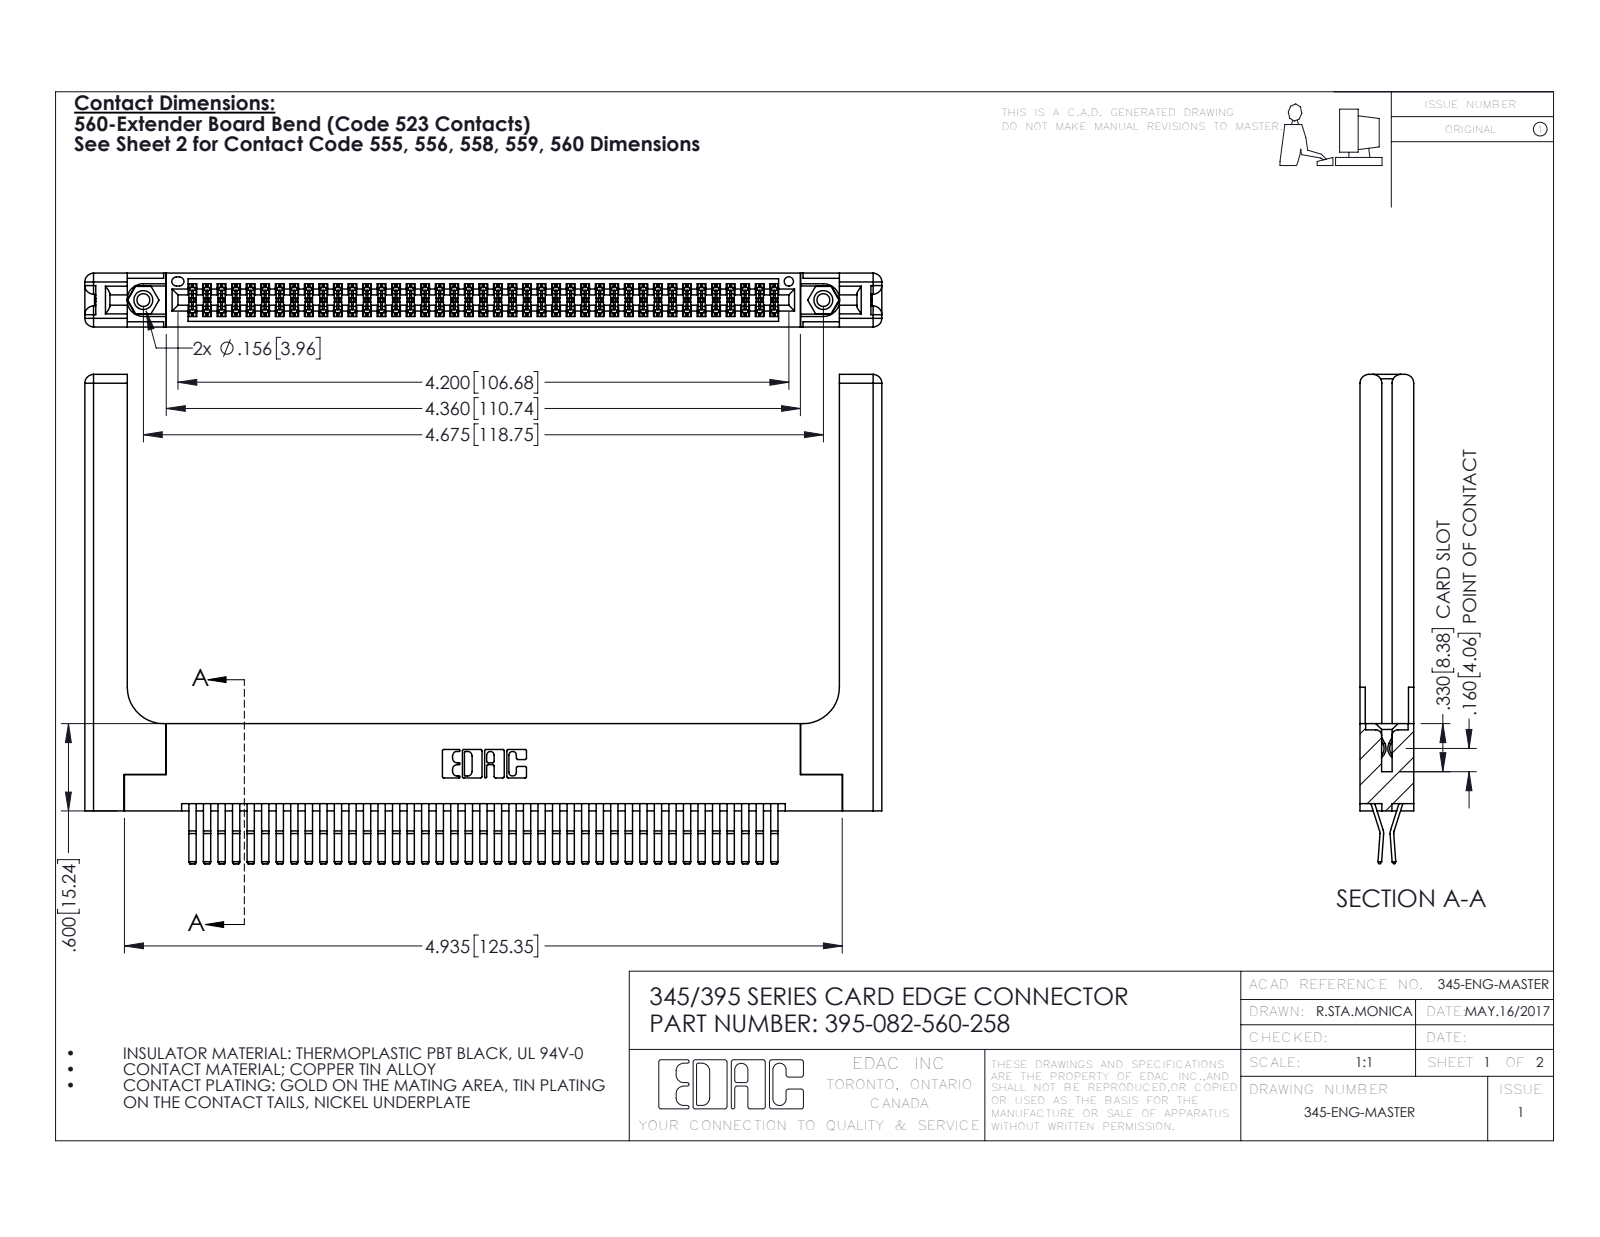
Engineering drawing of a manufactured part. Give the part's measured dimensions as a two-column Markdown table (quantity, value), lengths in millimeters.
| quantity | value |
| --- | --- |
| part name | 345-292-001_560 Tail; 395-082-560-258; 345-220-058_345-220-058; 345-250-001_345-250-001-102 (+1 more) |
| STEP written by | SolidWorks 2016 (CONFIG_CONTROL_DESIGN) |
| units | millimeters |
| bodies | 87 solids, 4646 faces (2934 planar, 1652 cylindrical, 60 other) |
| overall size | 139.2 × 85.4 × 9.4 |
| volume | 22 520 mm³ |
| surface area | 27 190 mm² |
| round holes (diameter × count) | 2.3 × 2, 3.2 × 2, 4 × 2, 1.6 × 1 |
| round bosses / shafts (diameter × count) | 3.9 × 2 |
| partial cylindrical surfaces (radius × count) | 0.2 × 123, 0.3 × 22, 1.5 × 16, 0.2 × 6, 0.8 × 6, 0.7 × 3, 0.3 × 2, 0.4 × 2 |
| main face-to-face distances | 1.8, 9.4, 7.6, 0.6, 5.1, 2.5, 6.9, 5.7, 3.8, 3.8 |
| hole center spacings | 6.9, 112.8, 118.7 |
